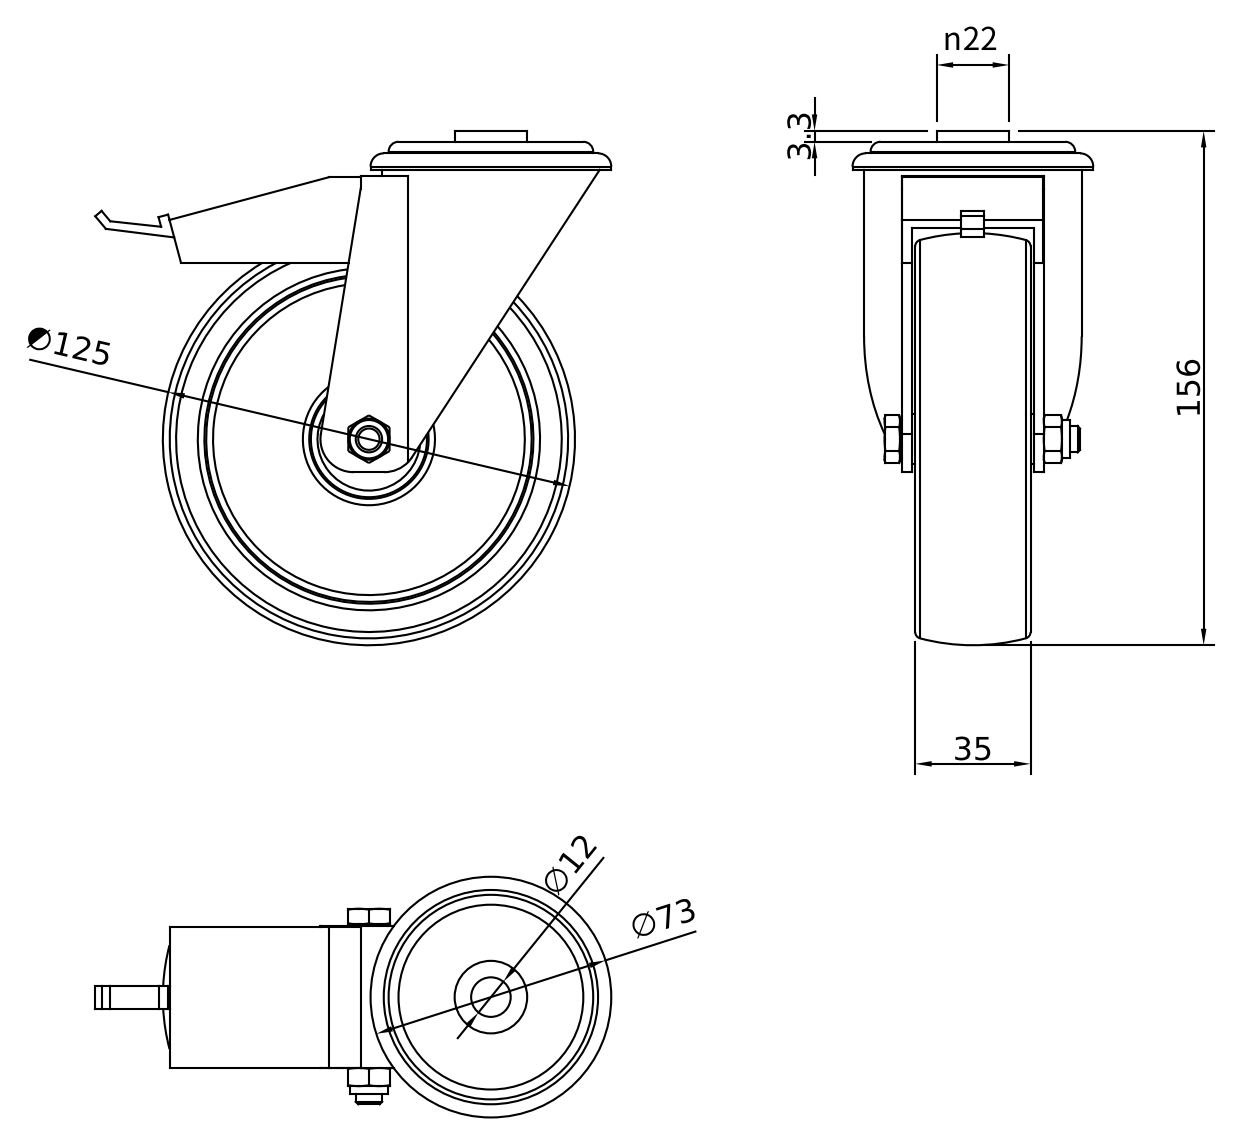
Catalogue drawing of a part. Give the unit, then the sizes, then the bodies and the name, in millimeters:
Units: millimetres
Overall size (bounding box): 156.5 × 156 × 73
Round holes (diameter × count): ⌀9 ×1, ⌀12 ×1, ⌀15 ×1, ⌀61 ×1
Round bosses / shafts (diameter × count): ⌀73 ×1, ⌀66 ×1, ⌀62.05 ×1, ⌀22 ×1, ⌀11.63 ×1, ⌀8 ×1
Partial cylindrical surfaces — rounded edges, fillets, slot ends (radius × count): R10 ×2
Main face-to-face distances: 36, 1, 40, 3, 4, 39, 37, 35, 10.7, 42.9
Volume: 310 060 mm³ · Surface area: 91 588 mm²
Bodies: 3 solids, 129 faces (65 planar, 20 cylindrical, 44 other)
Part name (STEP PRODUCT): CRUST0000187; 440000025958; 440000025957; 440000025956
STEP written by: Autodesk Inventor 2022 (AUTOMOTIVE_DESIGN)
